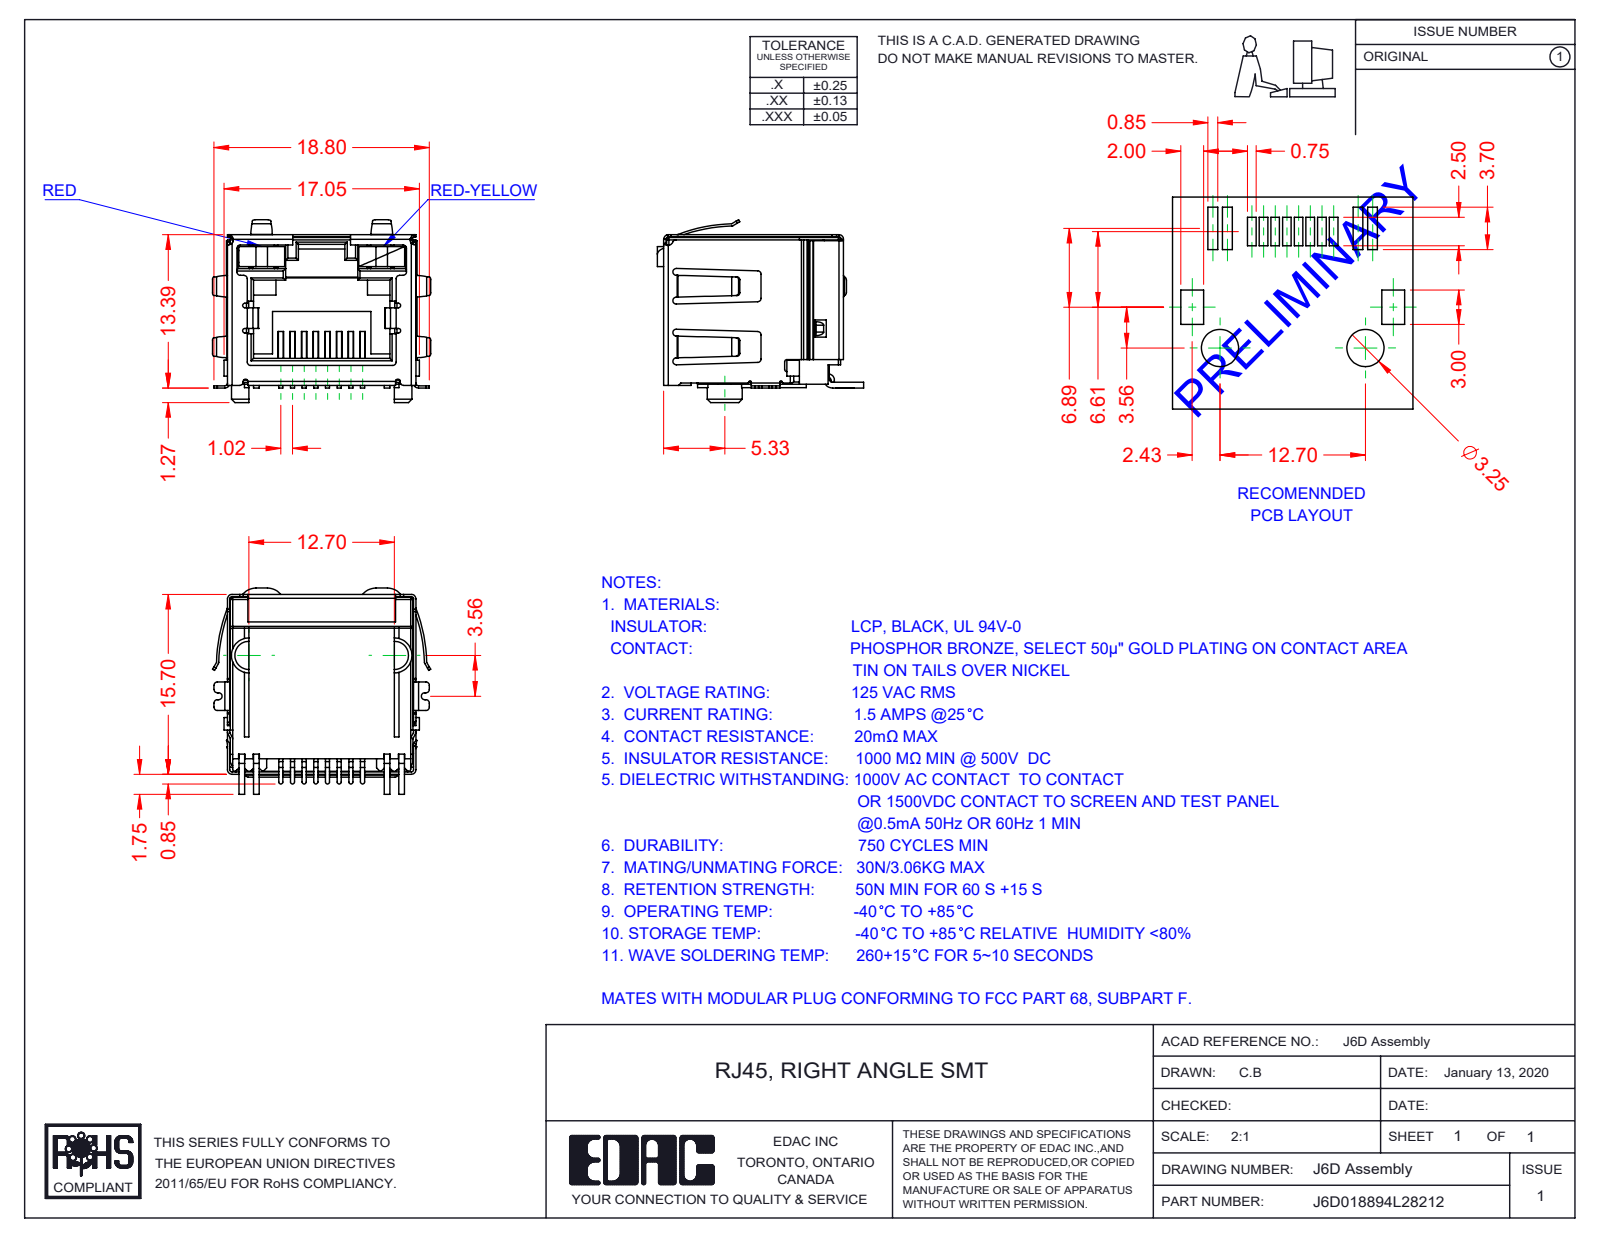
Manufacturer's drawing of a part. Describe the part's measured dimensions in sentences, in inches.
The part is named "6D Shield_LED - EMI; 6D LED LH_2-Red; J6D018894L28212; 6D LED RH_8-Red-Yellow (+2 more)". Its 3-D file was written by "SolidWorks 2016 (CONFIG_CONTROL_DESIGN)". It is 12 solids with 1031 faces: 702 planar, 284 cylindrical and 45 other. Overall it measures 0.75 by 0.709 by 0.628 inches. Its volume is 0.109 cubic inches and its surface area 7.434 square inches. Partial cylindrical surfaces (rounded edges, fillets, slot ends): 55 of radius 0.012, 40 of radius 0.008, 19 of radius 0.016, 16 of radius 0.01, 12 of radius 0.004, 8 of radius 0.006, 8 of radius 0.007, 6 of radius 0.02. The main face-to-face distances are 0.63, 0.638, 0.64, 0.089, 0.039, 0.628, 0.504, 0.018, 0.514, 0.417.
